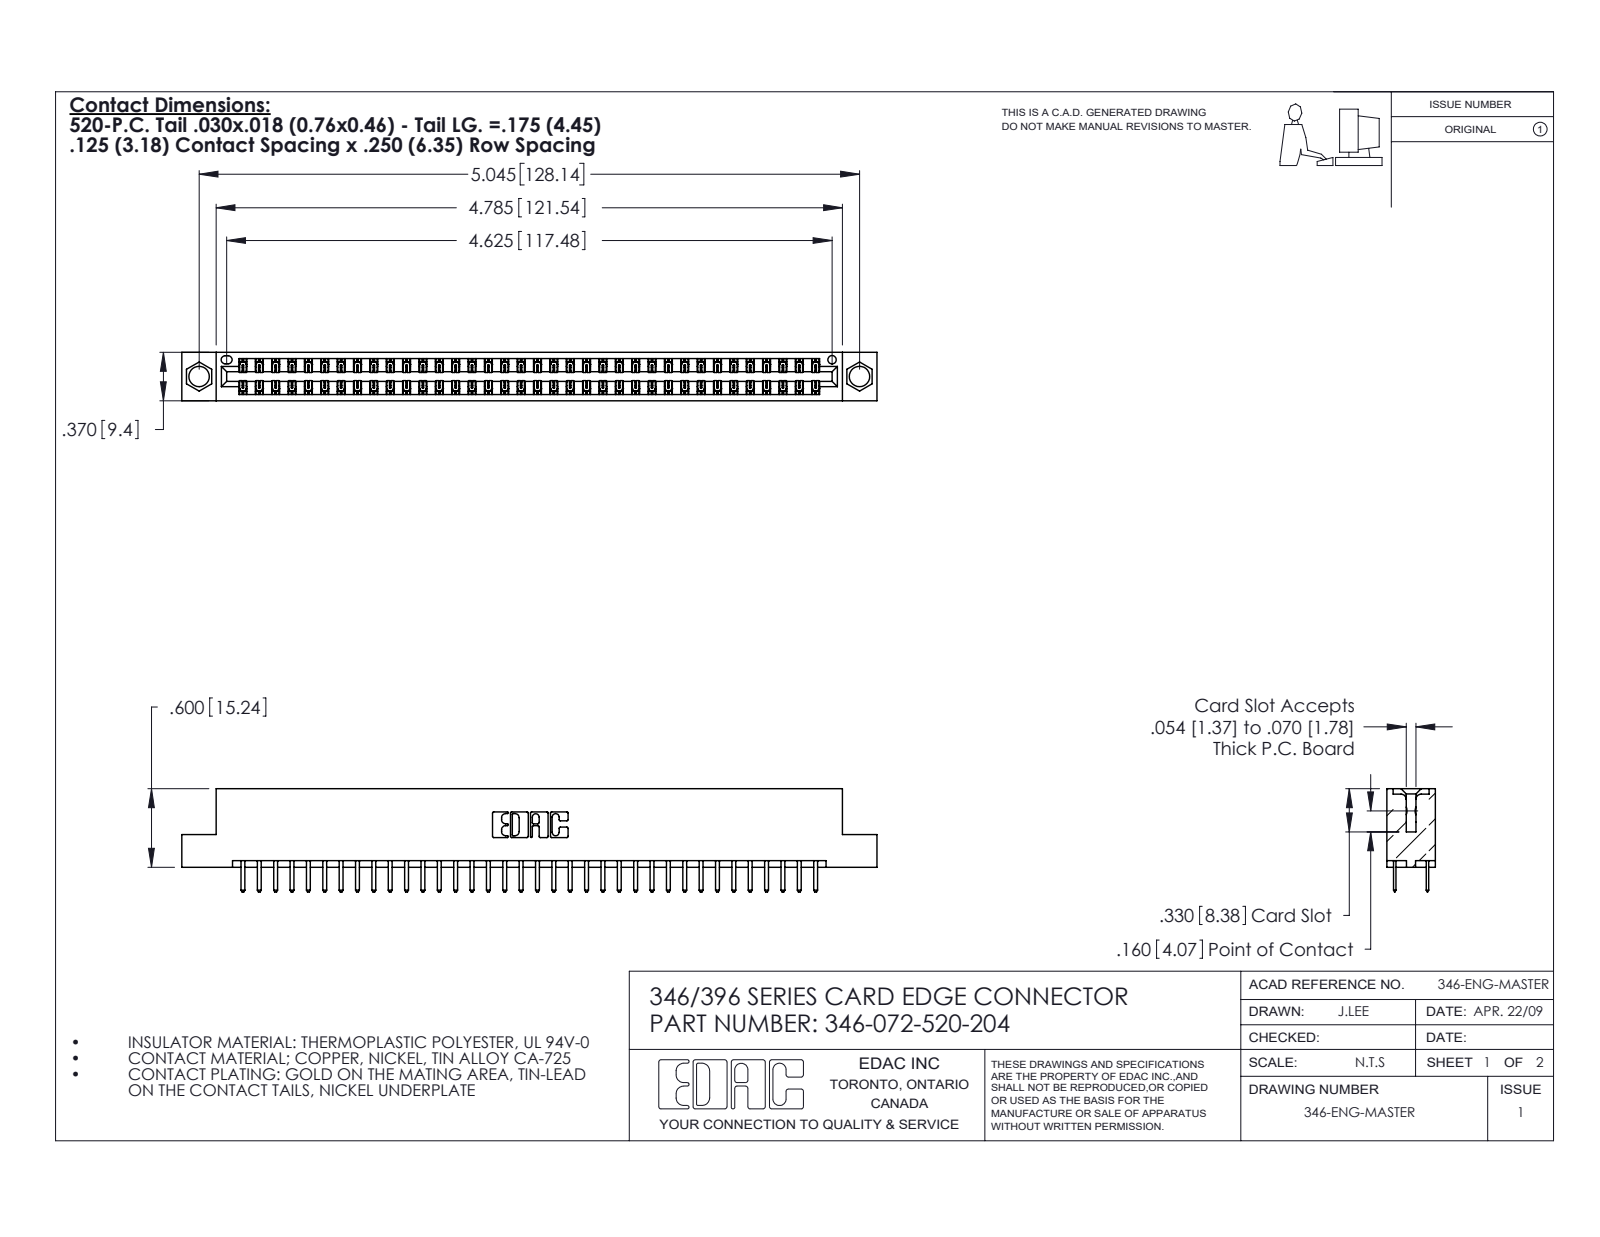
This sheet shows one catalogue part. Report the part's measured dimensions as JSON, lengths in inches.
{"part_name": "346 Part_Flush Mounting Lugs - 0.156 Dia-TH; 345-292-001_345-293-120; 346-072-520-204", "step_written_by": "SolidWorks 2020 (CONFIG_CONTROL_DESIGN)", "units": "inches", "bodies": {"solids": 73, "faces": 4168, "planar": 2754, "cylindrical": 1414, "other": 0}, "overall_size": [5.31, 0.788, 0.37], "volume_in3": 0.791, "surface_area_in2": 27.13, "round_holes": [[0.156, 2], [0.064, 1]], "partial_cylinders_radius": [[0.006, 108], [0.01, 76], [0.01, 22], [0.007, 6], [0.031, 6], [0.026, 3], [0.014, 2], [0.022, 2]], "face_to_face_distances": [0.048, 0.322, 0.25, 0.37, 0.275, 0.072, 0.298, 0.025, 0.148, 0.222], "hole_center_spacings": [0.246, 4.836, 5.045]}
